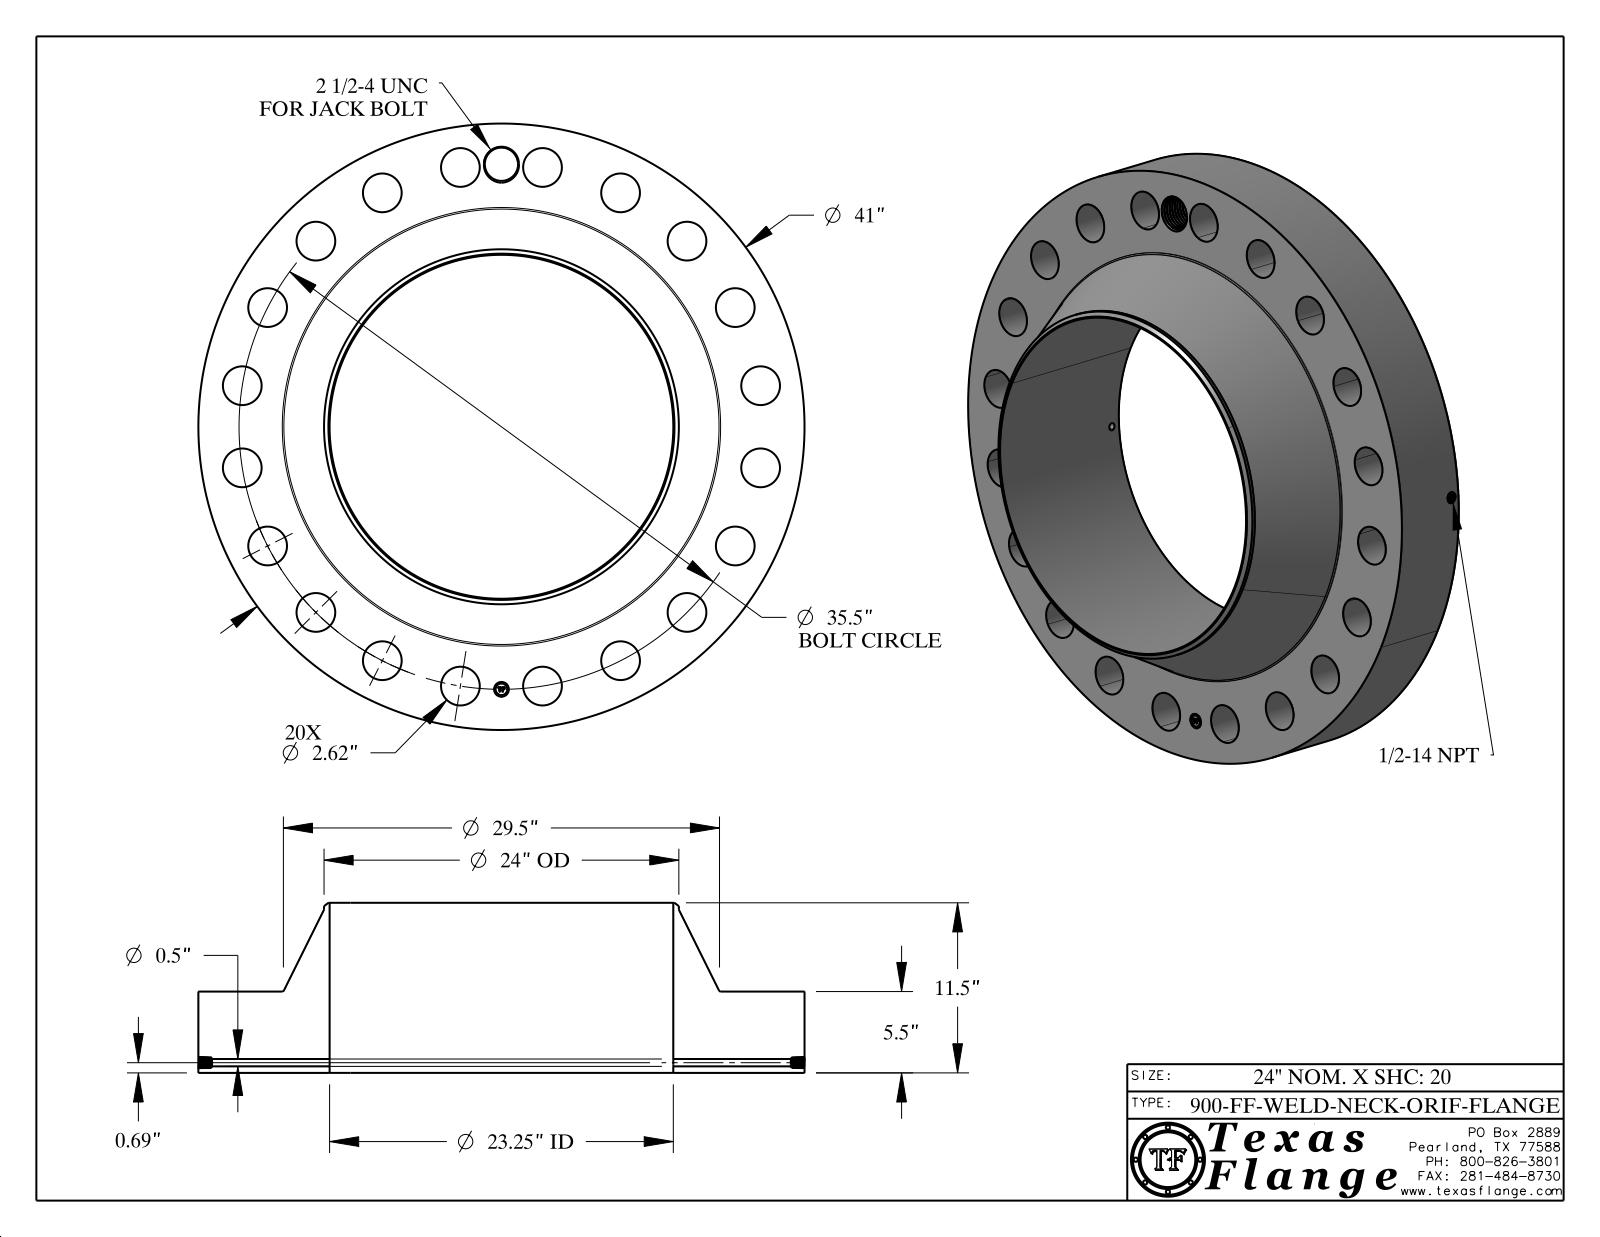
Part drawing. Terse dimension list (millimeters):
name: 900-FF-WELD-NECK
written by: CATIA V5 STEP AP214 (AUTOMOTIVE_DESIGN)
unit: mm
bodies: 1 solid, 832 faces (368 planar, 130 cylindrical, 334 other)
size: 1041.4 × 1041.4 × 292.1
volume: 83 360 000 mm³; area: 2 852 000 mm²
holes: 20× ⌀66.5, 1× ⌀12.7, 1× ⌀17.1, 1× ⌀25.4, 1× ⌀57.2, 1× ⌀590.6
bosses: 8× ⌀1.5, 1× ⌀1041.4, 1× ⌀609.6, 1× ⌀20
face distances: 139.7, 292.1, 152.4, 139.3, 0.4, 152.8, 7.6, 7.4, 1.4, 6.3
hole spacings: 450.9, 278.6, 637.6, 729.5, 803.4, 890.6, 530, 857.6
